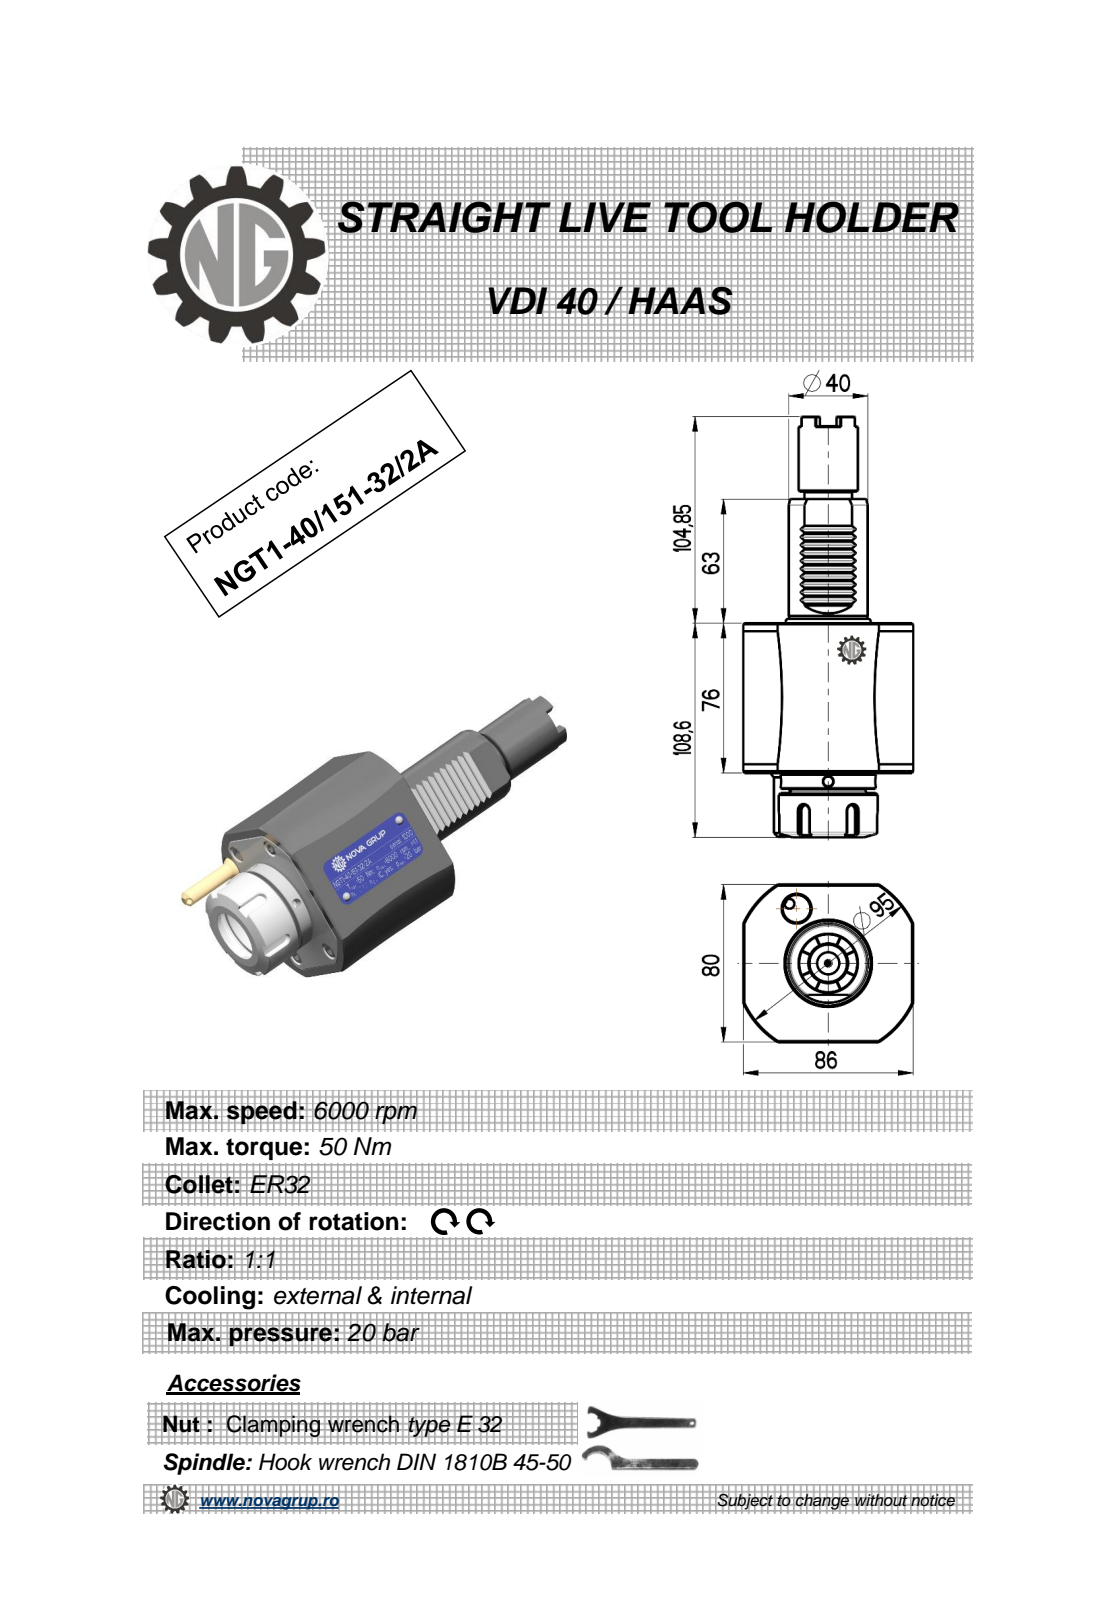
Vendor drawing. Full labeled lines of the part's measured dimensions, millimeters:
Part name (STEP PRODUCT): NGT1_40_151_32_1A
STEP written by: PRO/ENGINEER BY PARAMETRIC TECHNOLOGY CORPORATION, 2010280 (CONFIG_CONTROL_DESIGN)
Units: millimetres
Bodies: 1 solid, 316 faces (135 planar, 78 cylindrical, 103 other)
Overall size (bounding box): 213.45 × 86 × 81.6
Volume: 632 261 mm³ · Surface area: 56 597 mm²
Round holes (diameter × count): ⌀5 ×3, ⌀3 ×1, ⌀19.5 ×1, ⌀27 ×1
Round bosses / shafts (diameter × count): ⌀50 ×1, ⌀48 ×1, ⌀41.5 ×1, ⌀41 ×1, ⌀40 ×1, ⌀30 ×1, ⌀24 ×1, ⌀8 ×1
Partial cylindrical surfaces — rounded edges, fillets, slot ends (radius × count): R0.22 ×12, R0.3 ×10, R3 ×5, R47.5 ×1
Main face-to-face distances: 76, 80, 86, 2.83, 104.1, 28.1, 5.66, 63, 139, 167.1
Hole centre spacings: 40
